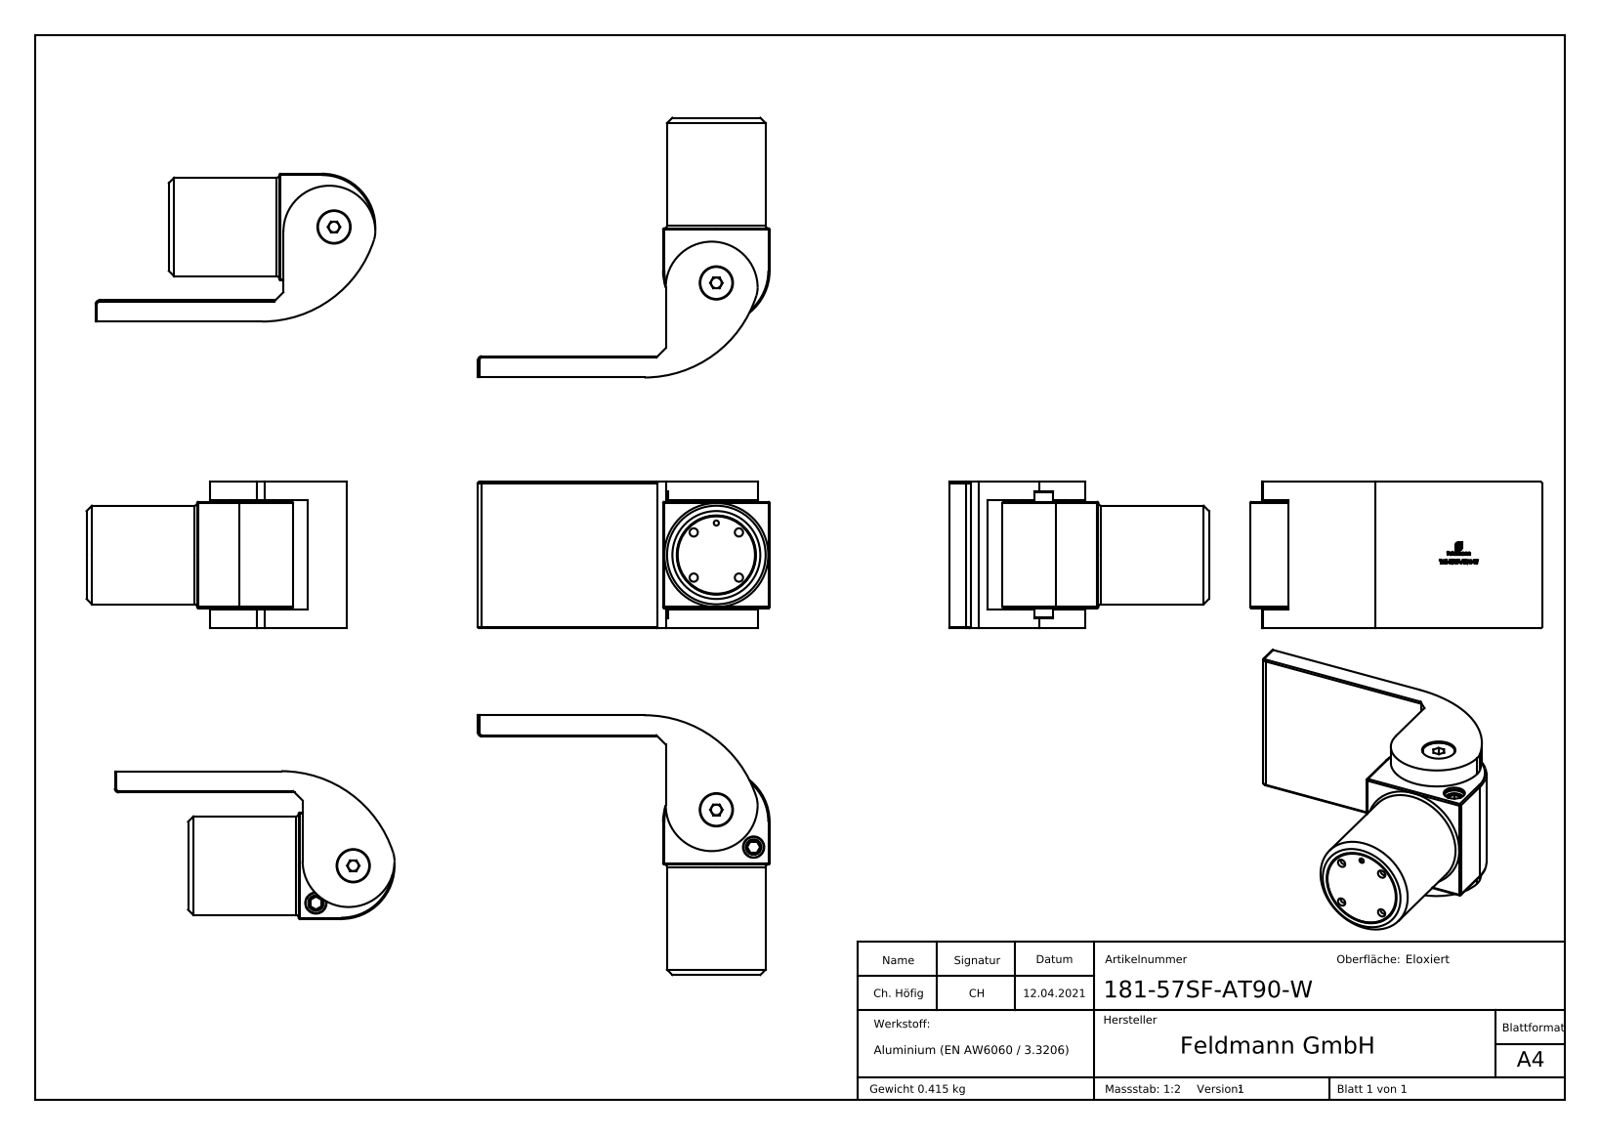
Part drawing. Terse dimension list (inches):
name: Teil1_181-57SF-AT90-W Teil1; 181-57SF-AT90-W; DIN-7991 M3-M10; Teil2 (+3 more)
written by: SolidWorks 2018 (CONFIG_CONTROL_DESIGN)
unit: in
bodies: 5 solids, 557 faces (285 planar, 82 cylindrical, 190 other)
size: 4.311 × 3.839 × 2.165
volume: 9.266 in³; area: 52.35 in²
holes: 4× ⌀0.122, 1× ⌀0.075, 1× ⌀0.197, 1× ⌀0.256, 1× ⌀0.315, 1× ⌀0.492, 1× ⌀0.618, 1× ⌀0.945, 1× ⌀1.169
bosses: 1× ⌀1.457, 1× ⌀1.161, 1× ⌀1.024, 1× ⌀0.929, 1× ⌀0.61, 1× ⌀0.472, 1× ⌀0.307, 1× ⌀0.236
rounds: 12× R0.02, 1× R0.059, 1× R0.394, 1× R0.679, 1× R0.787, 1× R1.737
face distances: 0.315, 1.89, 0.276, 2.165, 1.87, 0.02, 0.295, 1.594, 1.575, 0.571
hole spacings: 0.473, 0.669, 0.362, 0.873, 0.945, 0.472, 0.78
